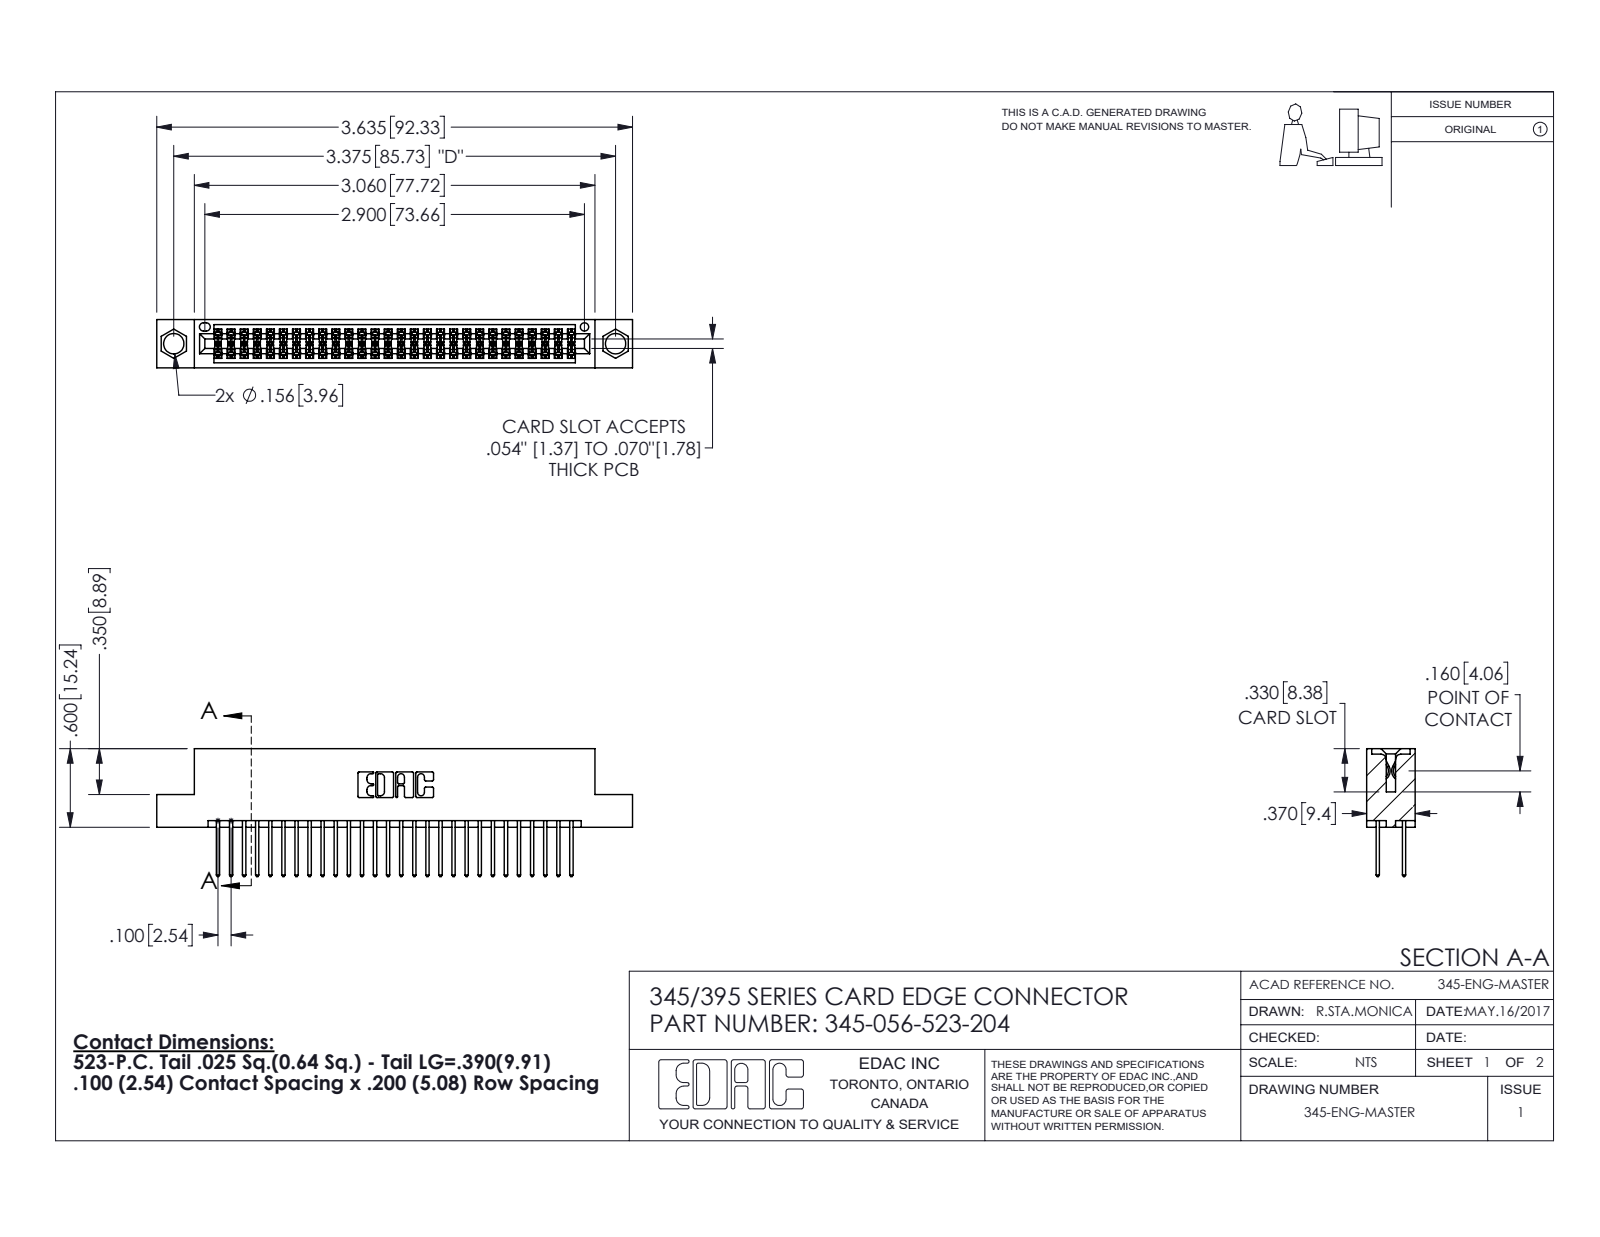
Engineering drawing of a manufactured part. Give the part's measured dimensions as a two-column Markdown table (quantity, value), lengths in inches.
| quantity | value |
| --- | --- |
| part name | 345-292-001_345-293-123; 345-056-523-204; 345 Part_Flush Mounting Lugs - 0.156 Dia-TI |
| STEP written by | SolidWorks 2020 (CONFIG_CONTROL_DESIGN) |
| units | inches |
| bodies | 57 solids, 2940 faces (1942 planar, 998 cylindrical, 0 other) |
| overall size | 3.635 × 0.977 × 0.37 |
| volume | 0.54 in³ |
| surface area | 20.42 in² |
| round holes (diameter × count) | 0.156 × 2, 0.064 × 1 |
| partial cylindrical surfaces (radius × count) | 0.006 × 84, 0.01 × 56, 0.01 × 22, 0.007 × 6, 0.031 × 6, 0.026 × 3, 0.014 × 2, 0.019 × 2 |
| main face-to-face distances | 0.298, 0.072, 0.2, 0.098, 0.272, 0.025, 0.37, 0.225, 0.175, 0.149 |
| hole center spacings | 0.27, 3.14, 3.375 |
